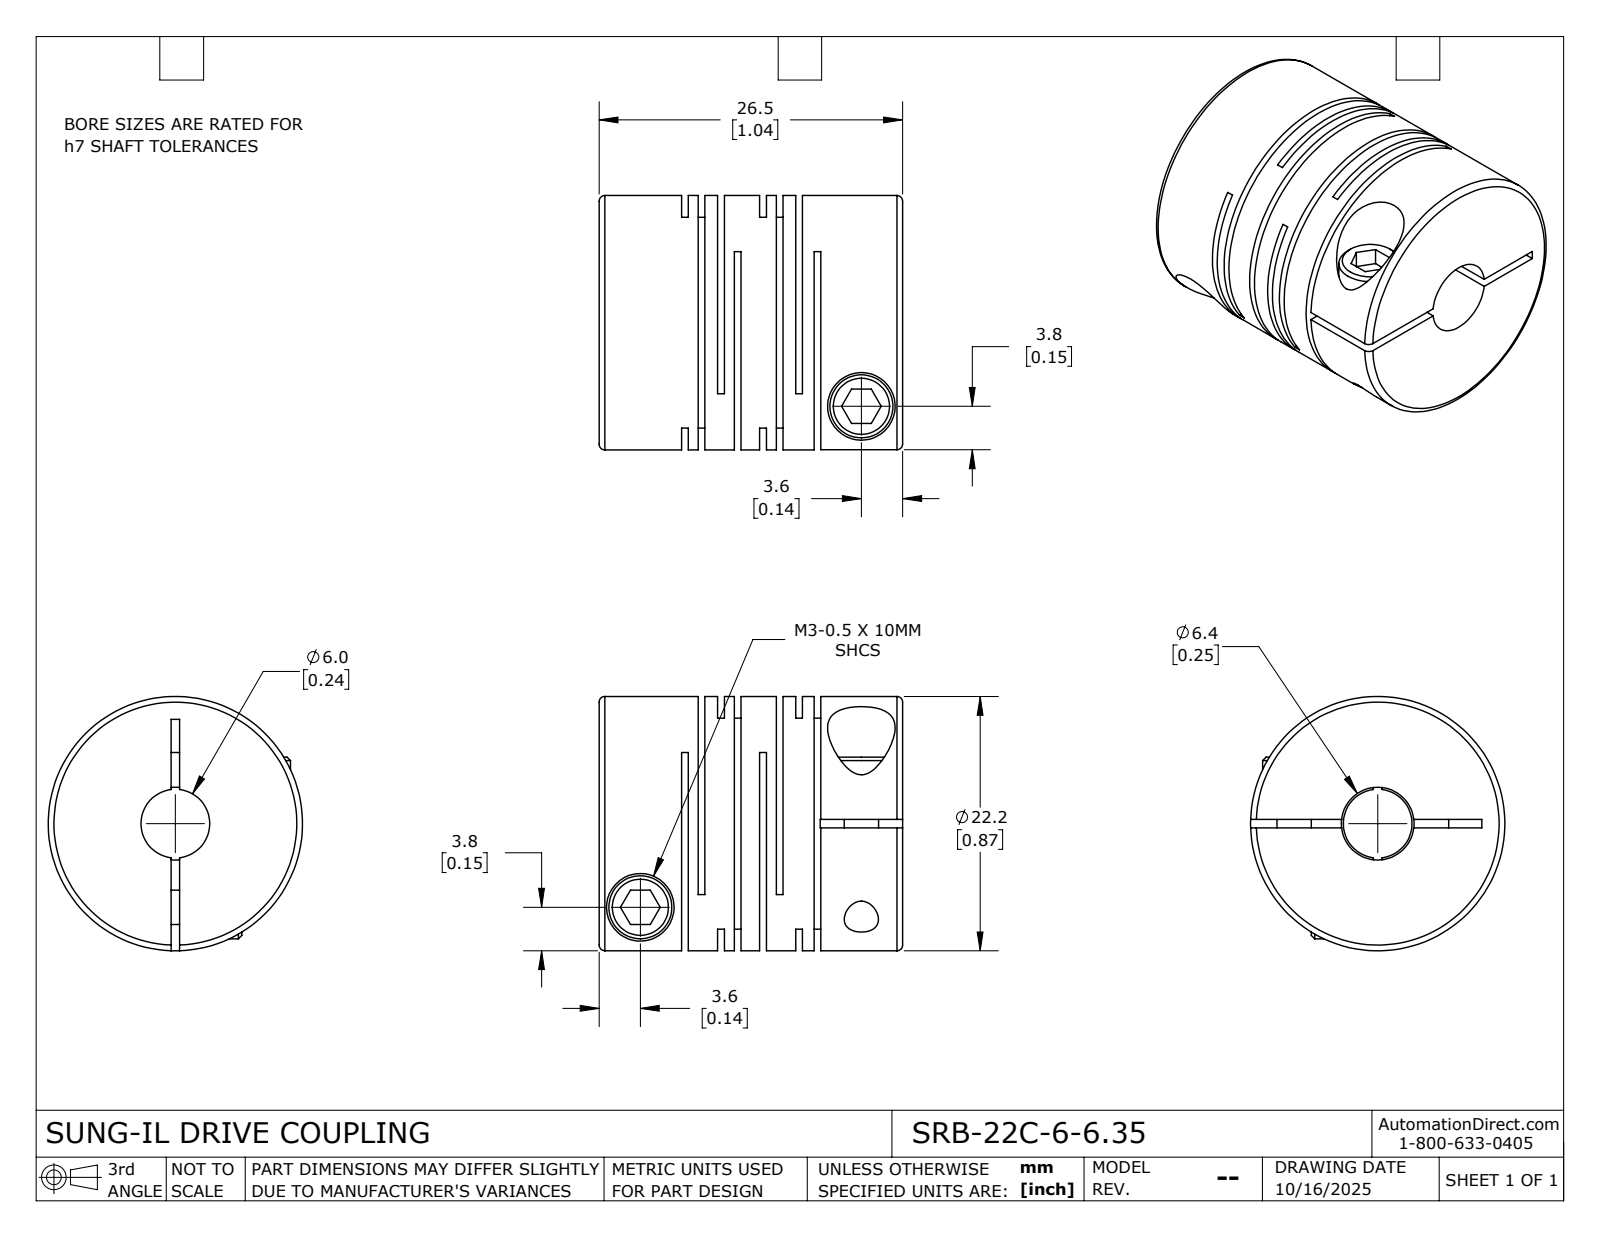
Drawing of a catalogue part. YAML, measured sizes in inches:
part_name: "SRB-22C-6-6.35"
step_written_by: "SolidWorks 2024 (CONFIG_CONTROL_DESIGN)"
units: inches
bodies: {solids: 1, faces: 115, planar: 60, cylindrical: 42, other: 13}
overall_size: [1.043, 0.874, 0.874]
volume: 0.471
surface_area: 12.57
round_holes:
  - {diameter: 0.118, count: 2}
  - {diameter: 0.232, count: 2}
  - {diameter: 0.236, count: 1}
  - {diameter: 0.25, count: 1}
round_bosses_or_shafts:
  - {diameter: 0.217, count: 2}
  - {diameter: 0.874, count: 1}
face_to_face_distances: [0.023, 0.124, 0.269, 0.057, 0.211, 0.067, 0.144, 0.245, 0.034, 0.101]
